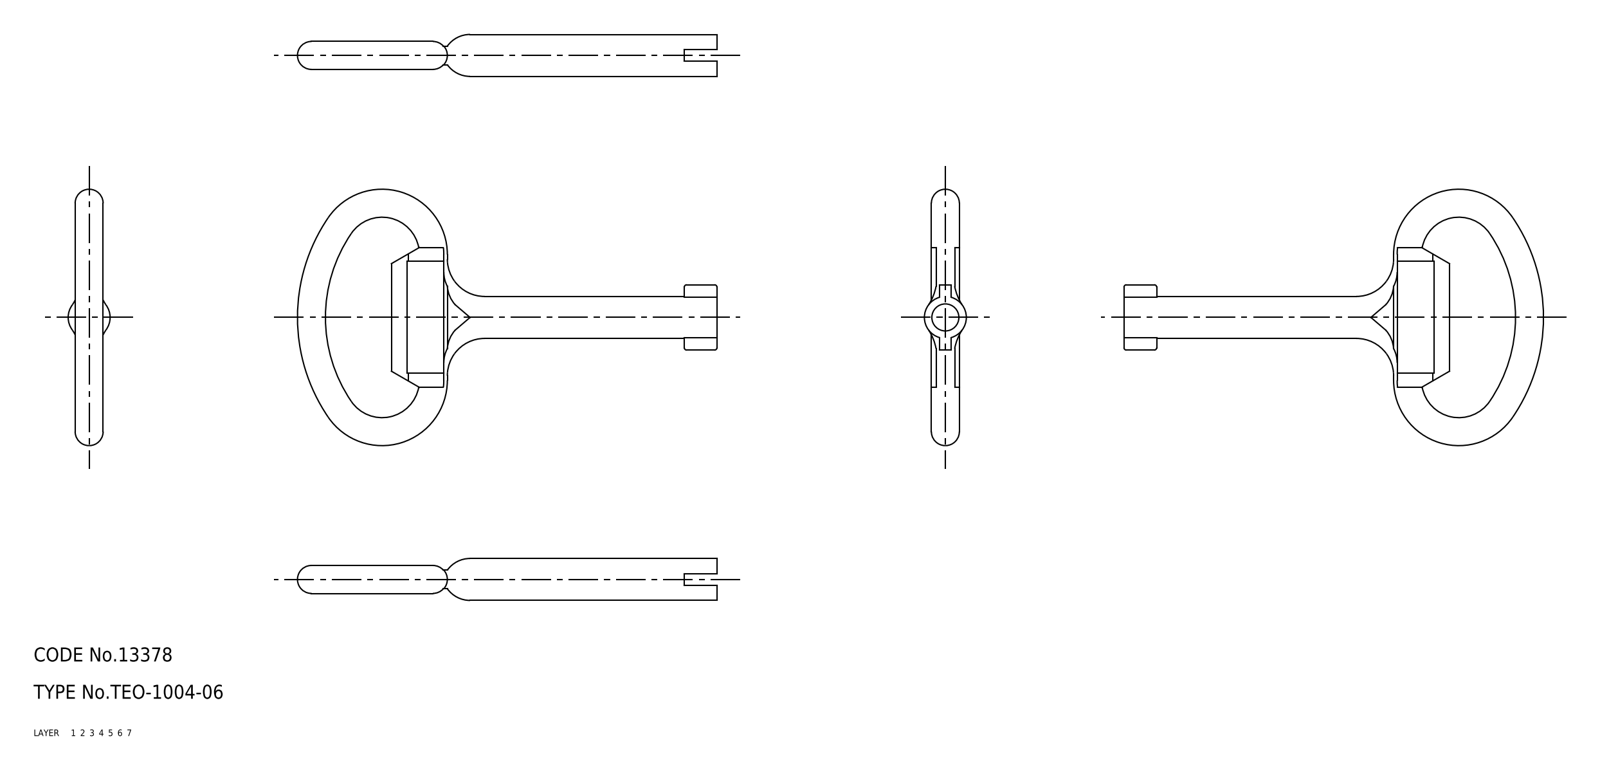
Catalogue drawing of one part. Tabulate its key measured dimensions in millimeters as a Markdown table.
| quantity | value |
| --- | --- |
| part name | key |
| STEP written by | CADfix (AUTOMOTIVE_DESIGN) |
| units | millimeters |
| bodies | 1 solid, 89 faces (0 planar, 0 cylindrical, 89 other) |
| overall size | 90 × 55 × 9 |
| volume | 7 230 mm³ |
| surface area | 4 709 mm² |
